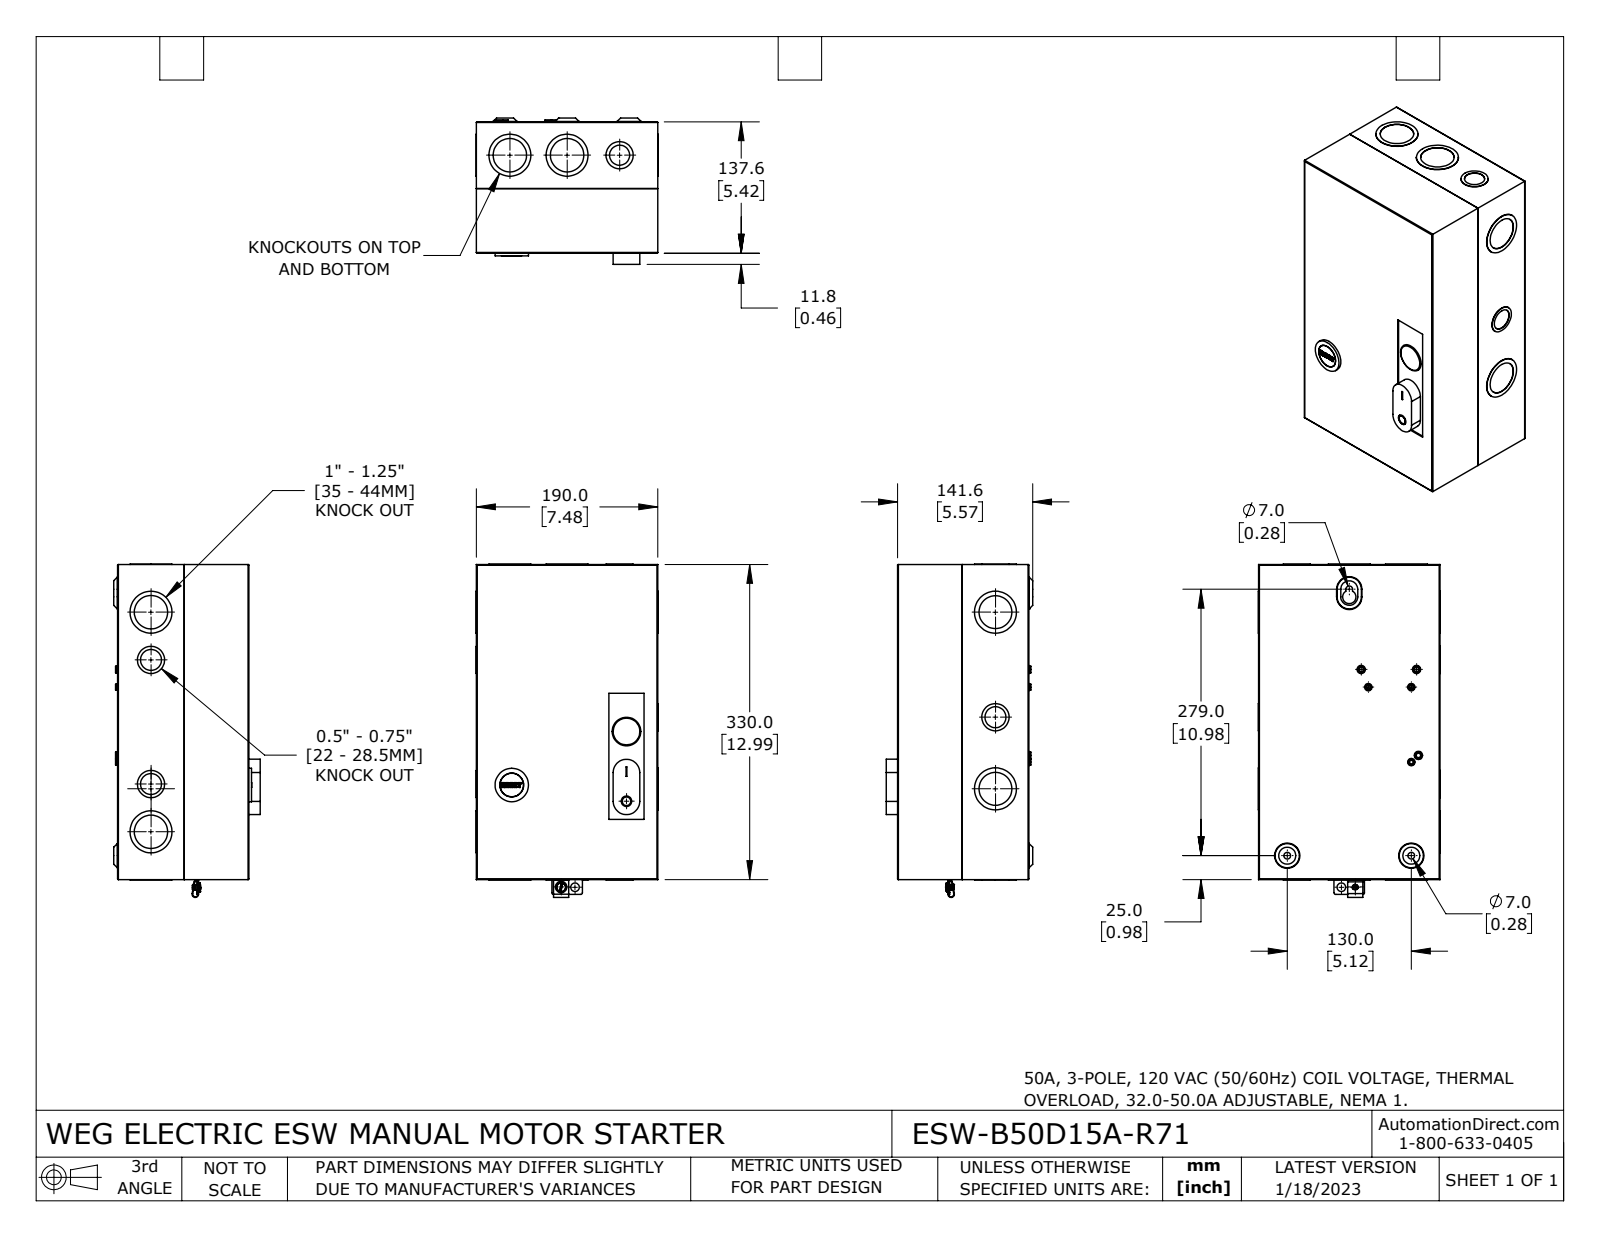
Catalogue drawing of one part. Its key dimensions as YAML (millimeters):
part_name: "ESW-B50D15A-R71"
step_written_by: "SolidWorks 2021 (CONFIG_CONTROL_DESIGN)"
units: millimeters
bodies: {solids: 7, faces: 435, planar: 161, cylindrical: 221, other: 53}
overall_size: [349, 190.6, 153.4]
volume: 402800
surface_area: 604300
round_holes:
  - {diameter: 35, count: 4}
  - {diameter: 3.7, count: 3}
  - {diameter: 4.6, count: 3}
  - {diameter: 7, count: 2}
  - {diameter: 22, count: 2}
  - {diameter: 22.5, count: 2}
  - {diameter: 34.5, count: 2}
  - {diameter: 6.5, count: 1}
  - {diameter: 7.1, count: 1}
  - {diameter: 9, count: 1}
  - {diameter: 11, count: 1}
  - {diameter: 11.9, count: 1}
round_bosses_or_shafts:
  - {diameter: 44, count: 4}
  - {diameter: 28.5, count: 3}
  - {diameter: 7.1, count: 3}
  - {diameter: 6.1, count: 3}
  - {diameter: 44, count: 2}
  - {diameter: 35, count: 1}
  - {diameter: 30.3, count: 1}
  - {diameter: 29.2, count: 1}
partial_cylinders:
  - {radius: 0.1, count: 34}
  - {radius: 0.8, count: 8}
  - {radius: 2, count: 3}
  - {radius: 3.5, count: 3}
  - {radius: 1.5, count: 2}
  - {radius: 1.9, count: 2}
  - {radius: 2.7, count: 2}
  - {radius: 3.1, count: 2}
face_to_face_distances: [1.2, 136.4, 188.8, 135.2, 137.6, 328.8, 187.6, 190, 1.8, 327.6]
hole_center_spacings: [14.5, 45, 50, 58, 60, 130, 180, 278.7]
